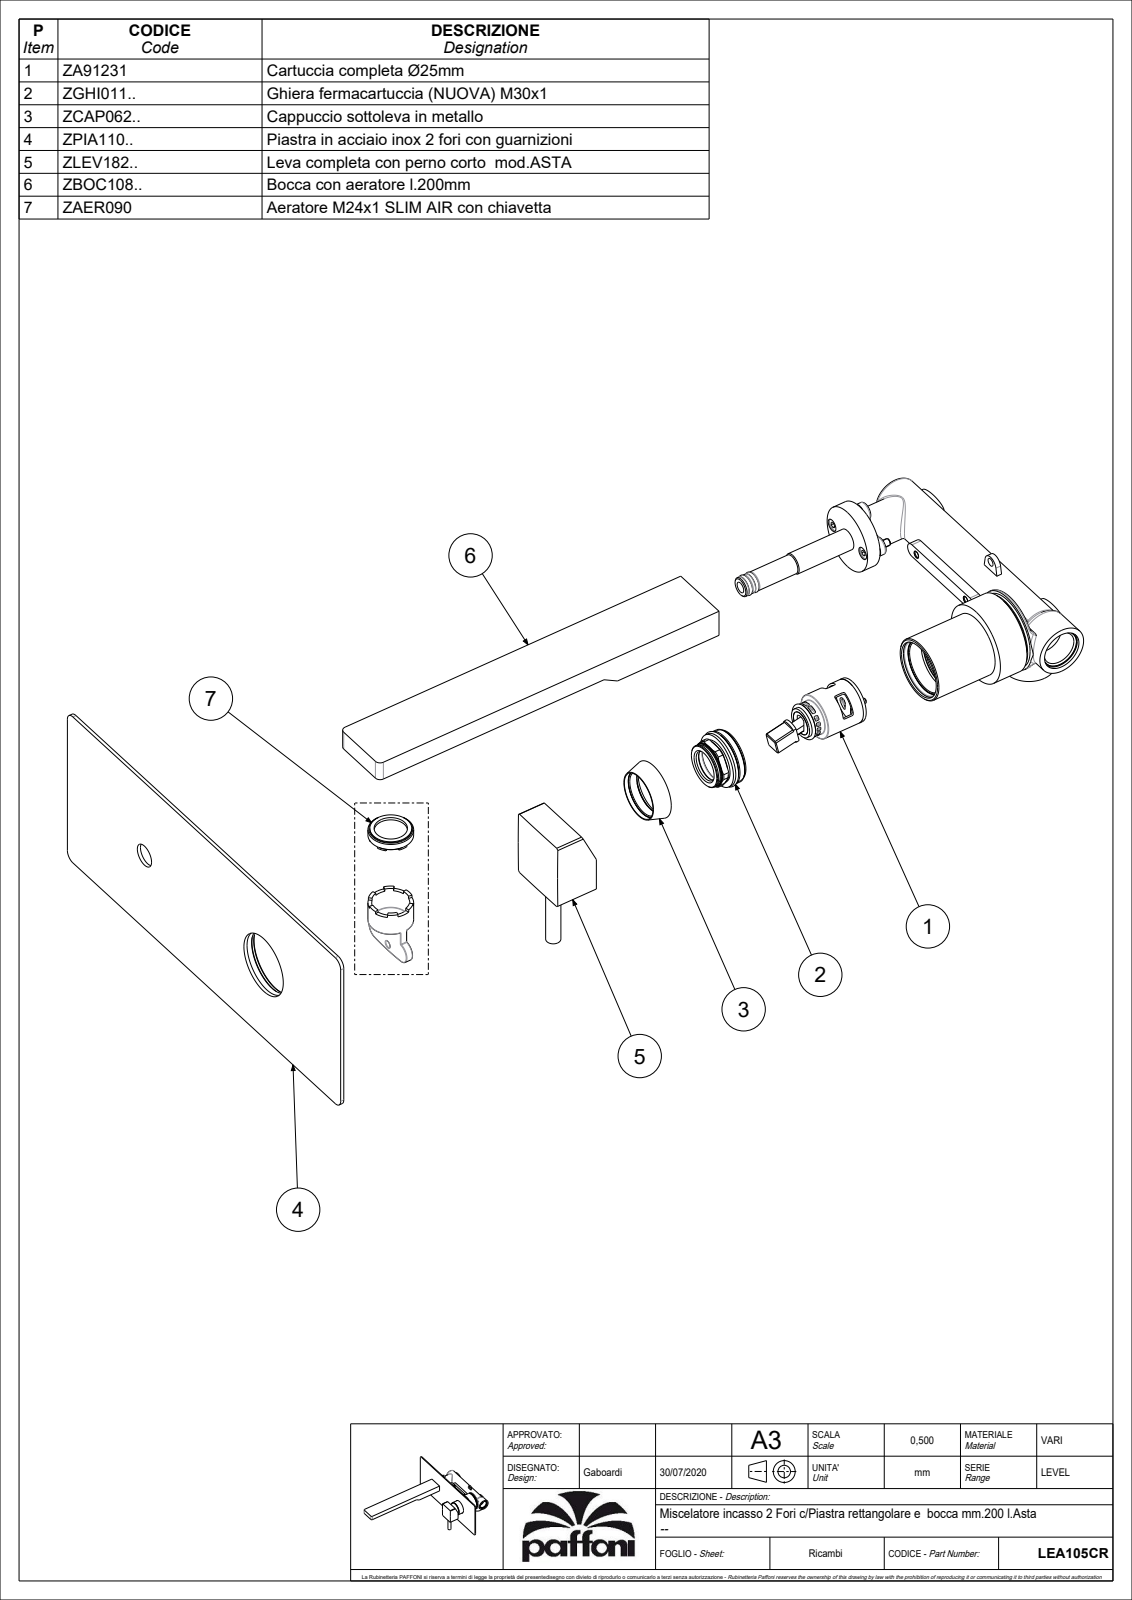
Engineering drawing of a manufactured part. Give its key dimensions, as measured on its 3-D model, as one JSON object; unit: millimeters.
{"part_name": "LEA105CR", "step_written_by": "CREO PARAMETRIC BY PTC INC, 2020044 (CONFIG_CONTROL_DESIGN)", "units": "millimeters", "bodies": {"solids": 2, "faces": 677, "planar": 210, "cylindrical": 252, "other": 215}, "overall_size": [250, 220, 110.16], "volume_mm3": 174775, "surface_area_mm2": 102311, "round_holes": [[6, 2], [11, 2], [8.2, 1], [12, 1], [13, 1], [15, 1], [16.7, 1], [17, 1], [17.5, 1], [19.2, 1], [20.2, 1], [22.7, 1]], "round_bosses_or_shafts": [[35.2, 1], [30, 1], [27.7, 1], [25, 1], [23.8, 1], [22.5, 1], [20, 1], [19, 1]], "partial_cylinders_radius": [[0.5, 56], [1, 7], [2, 4], [5, 4], [2.1, 3], [2.5, 2], [3, 2], [3.5, 2]], "face_to_face_distances": [2, 11.5, 35, 5, 16.5, 41.75, 58.25, 73.5, 108.5, 144.5], "hole_center_spacings": [1.16, 109, 109.01, 198.32]}
